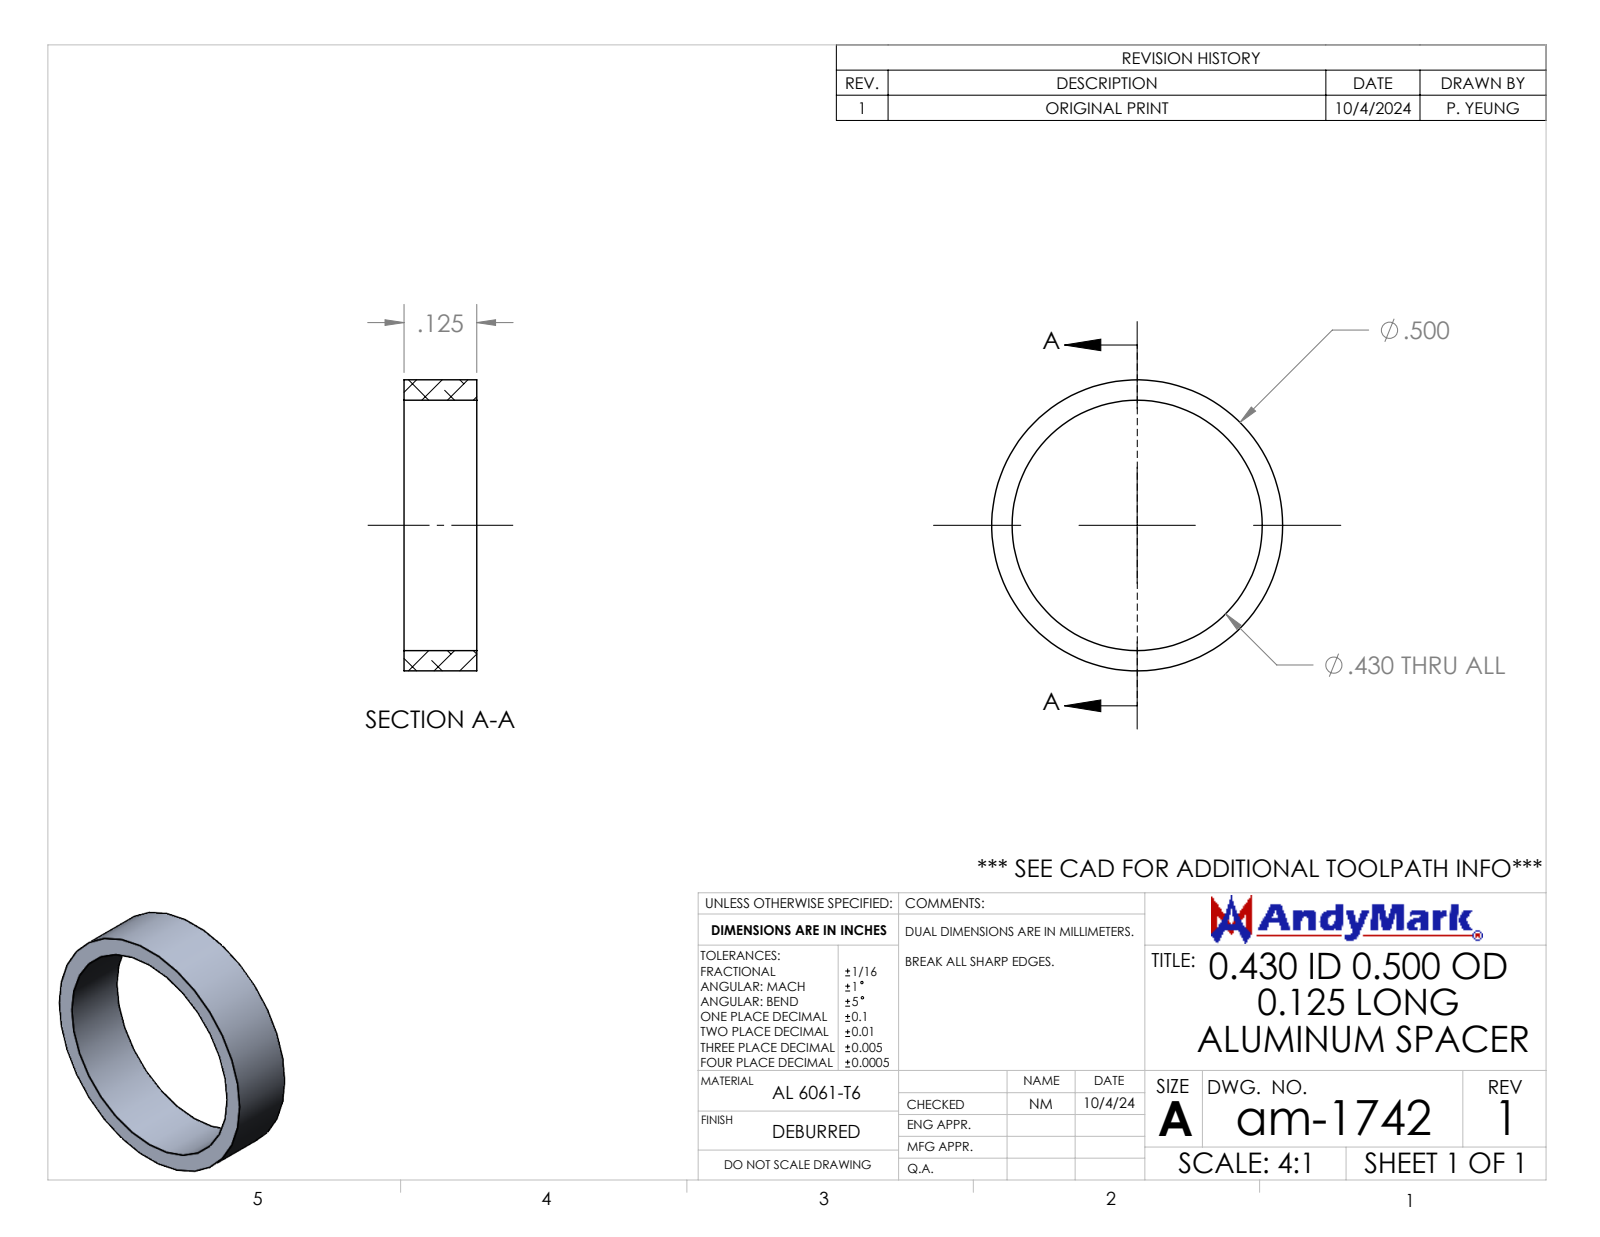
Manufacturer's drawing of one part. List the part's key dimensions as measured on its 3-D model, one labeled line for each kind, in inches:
Part name (STEP PRODUCT): am-1742 0.430 ID 0.500 OD 0.125 Long Aluminum Spacer
STEP written by: SolidWorks 2024 (AUTOMOTIVE_DESIGN)
Units: inches
Bodies: 1 solid, 6 faces (2 planar, 4 cylindrical, 0 other)
Overall size (bounding box): 0.5 × 0.5 × 0.125
Volume: 0.006 in³ · Surface area: 0.467 in²
Round holes (diameter × count): ⌀0.43 ×1
Round bosses / shafts (diameter × count): ⌀0.5 ×1
Main face-to-face distances: 0.125
